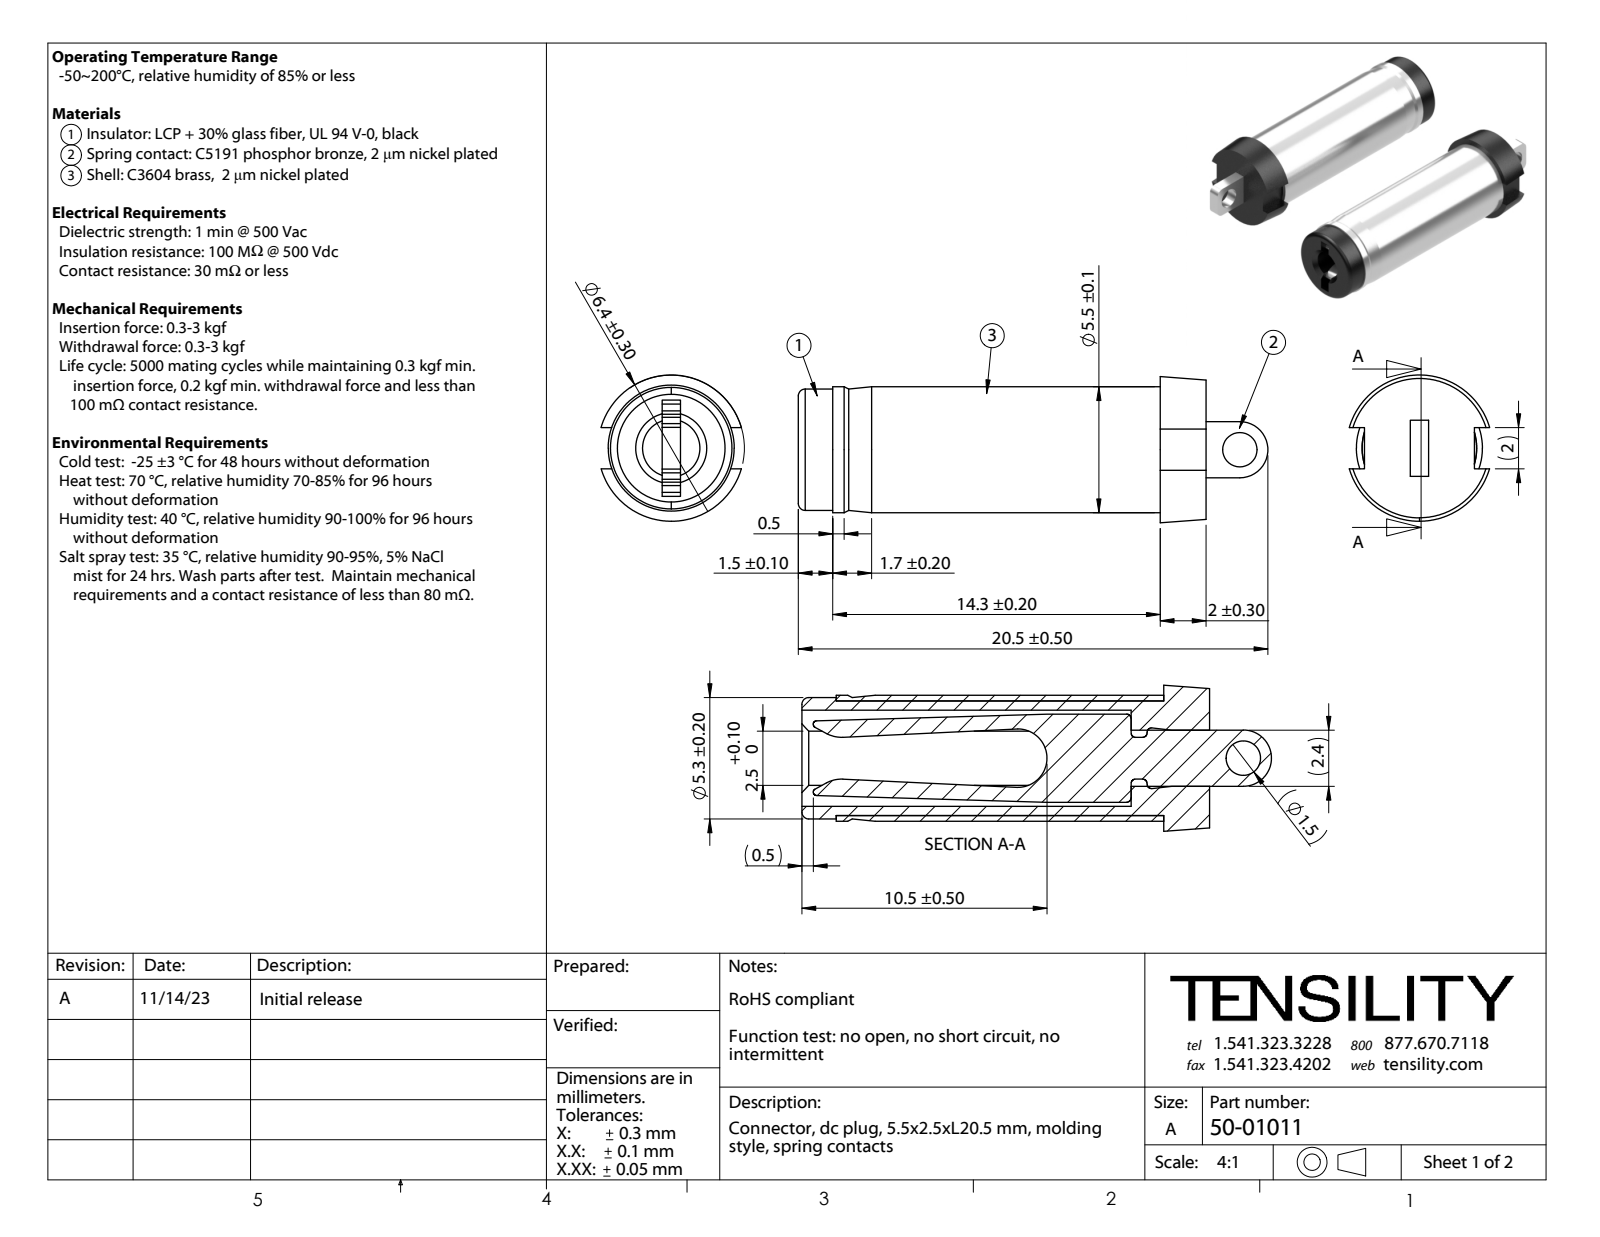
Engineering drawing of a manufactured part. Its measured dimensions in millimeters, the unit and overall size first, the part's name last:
Units: millimetres
Overall size (bounding box): 20.5 × 6.38 × 6.12
Round holes (diameter × count): ⌀1.5 ×1, ⌀5 ×1
Round bosses / shafts (diameter × count): ⌀5.5 ×1, ⌀5.3 ×1
Partial cylindrical surfaces — rounded edges, fillets, slot ends (radius × count): R0.2 ×8, R0.15 ×2, R1.41 ×2, R1.23 ×1, R1.25 ×1, R1.27 ×1
Main face-to-face distances: 0.8, 2, 4.2, 15.8, 17.8, 2.8, 1.5, 14.3, 16.3, 0.7
Volume: 363 mm³ · Surface area: 1 153 mm²
Bodies: 3 solids, 86 faces (45 planar, 30 cylindrical, 11 other)
Part name (STEP PRODUCT): 50-01011_revA
STEP written by: SolidWorks 2021 (CONFIG_CONTROL_DESIGN)
